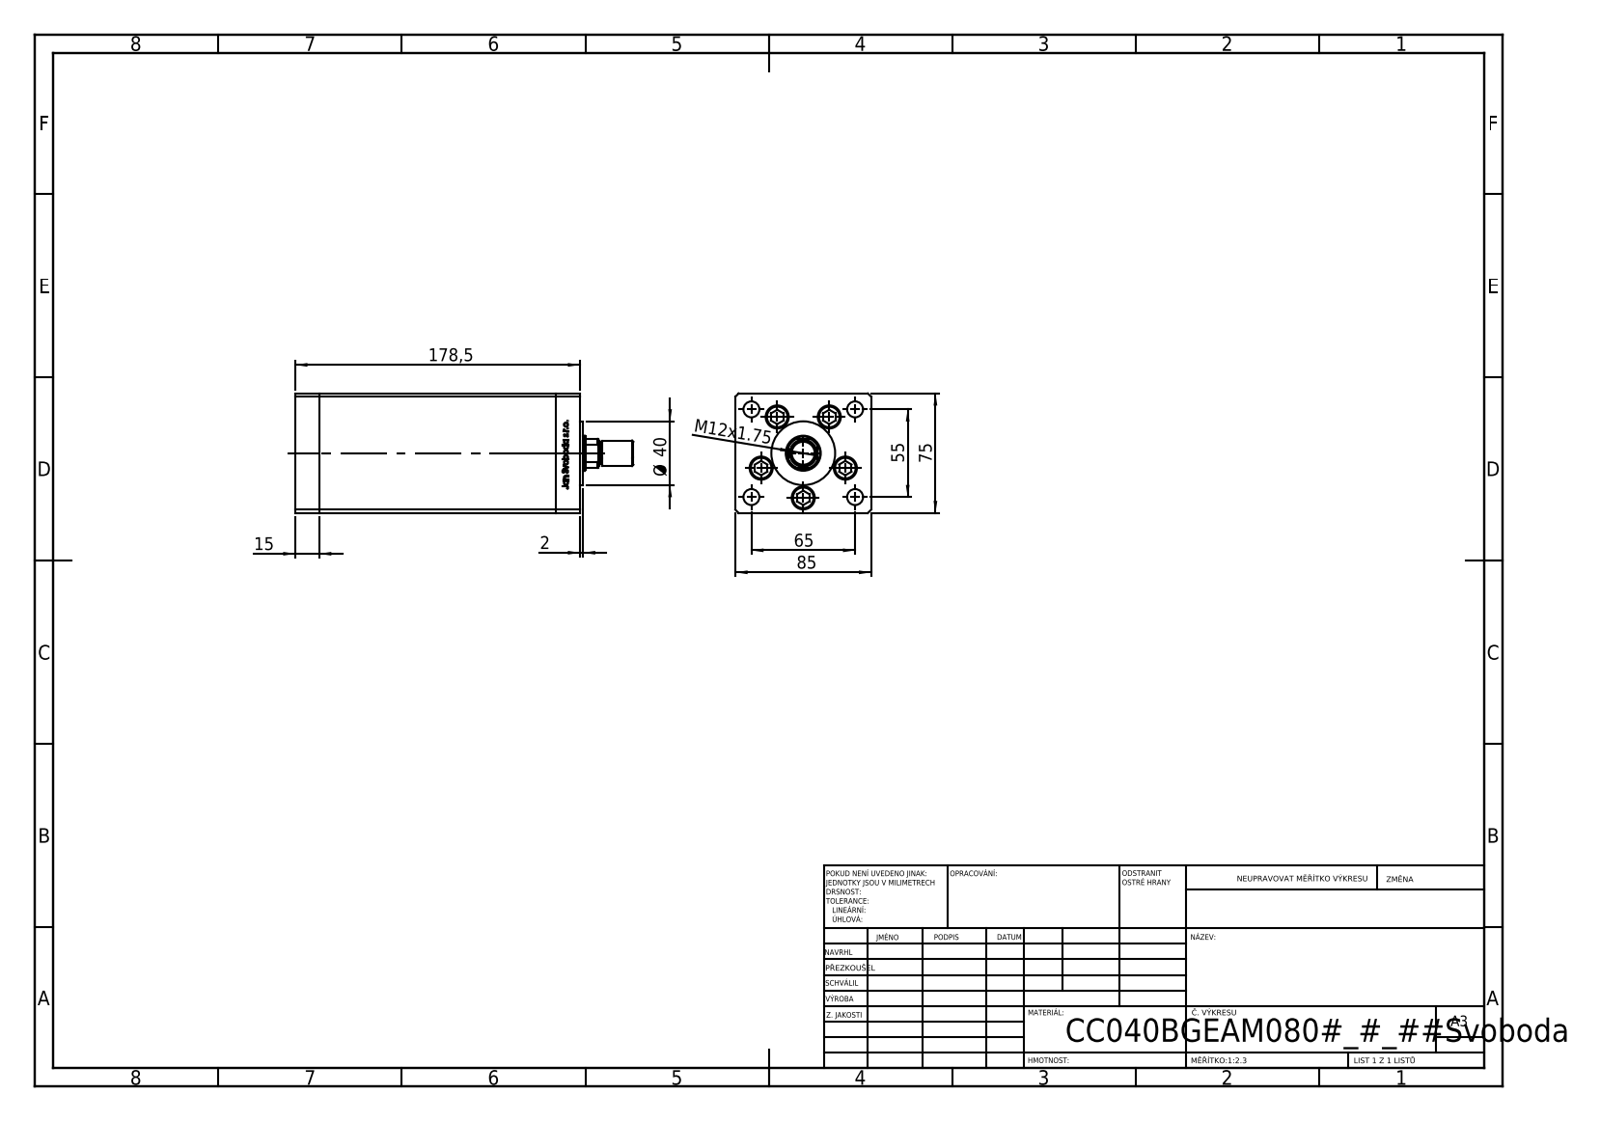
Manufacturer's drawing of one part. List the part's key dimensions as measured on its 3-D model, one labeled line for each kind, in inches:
Part name (STEP PRODUCT): V220C_FRONT_B; V220C_VC_B; ALLEN BOLT; V220CC_MALE_METRIC (+2 more)
STEP written by: SolidWorks 2019 (CONFIG_CONTROL_DESIGN)
Units: inches
Bodies: 15 solids, 1199 faces (468 planar, 151 cylindrical, 580 other)
Overall size (bounding box): 8.346 × 3.346 × 2.953
Volume: 62 in³ · Surface area: 251.2 in²
Round holes (diameter × count): ⌀0.433 ×5, ⌀0.571 ×5, ⌀0.394 ×4, ⌀0.079 ×2, ⌀0.518 ×2, ⌀0.531 ×1, ⌀0.866 ×1
Round bosses / shafts (diameter × count): ⌀0.315 ×5, ⌀1.575 ×1, ⌀0.63 ×1, ⌀0.551 ×1
Partial cylindrical surfaces — rounded edges, fillets, slot ends (radius × count): R0.037 ×2, R0.413 ×1
Main face-to-face distances: 3.346, 2.953, 0.591, 5.846, 6.437, 7.028, 1.348, 0.758, 5.089, 5.679
Hole centre spacings: 1.102, 1.676, 0.664, 0.755, 1.273, 1.28, 1.324, 1.47
